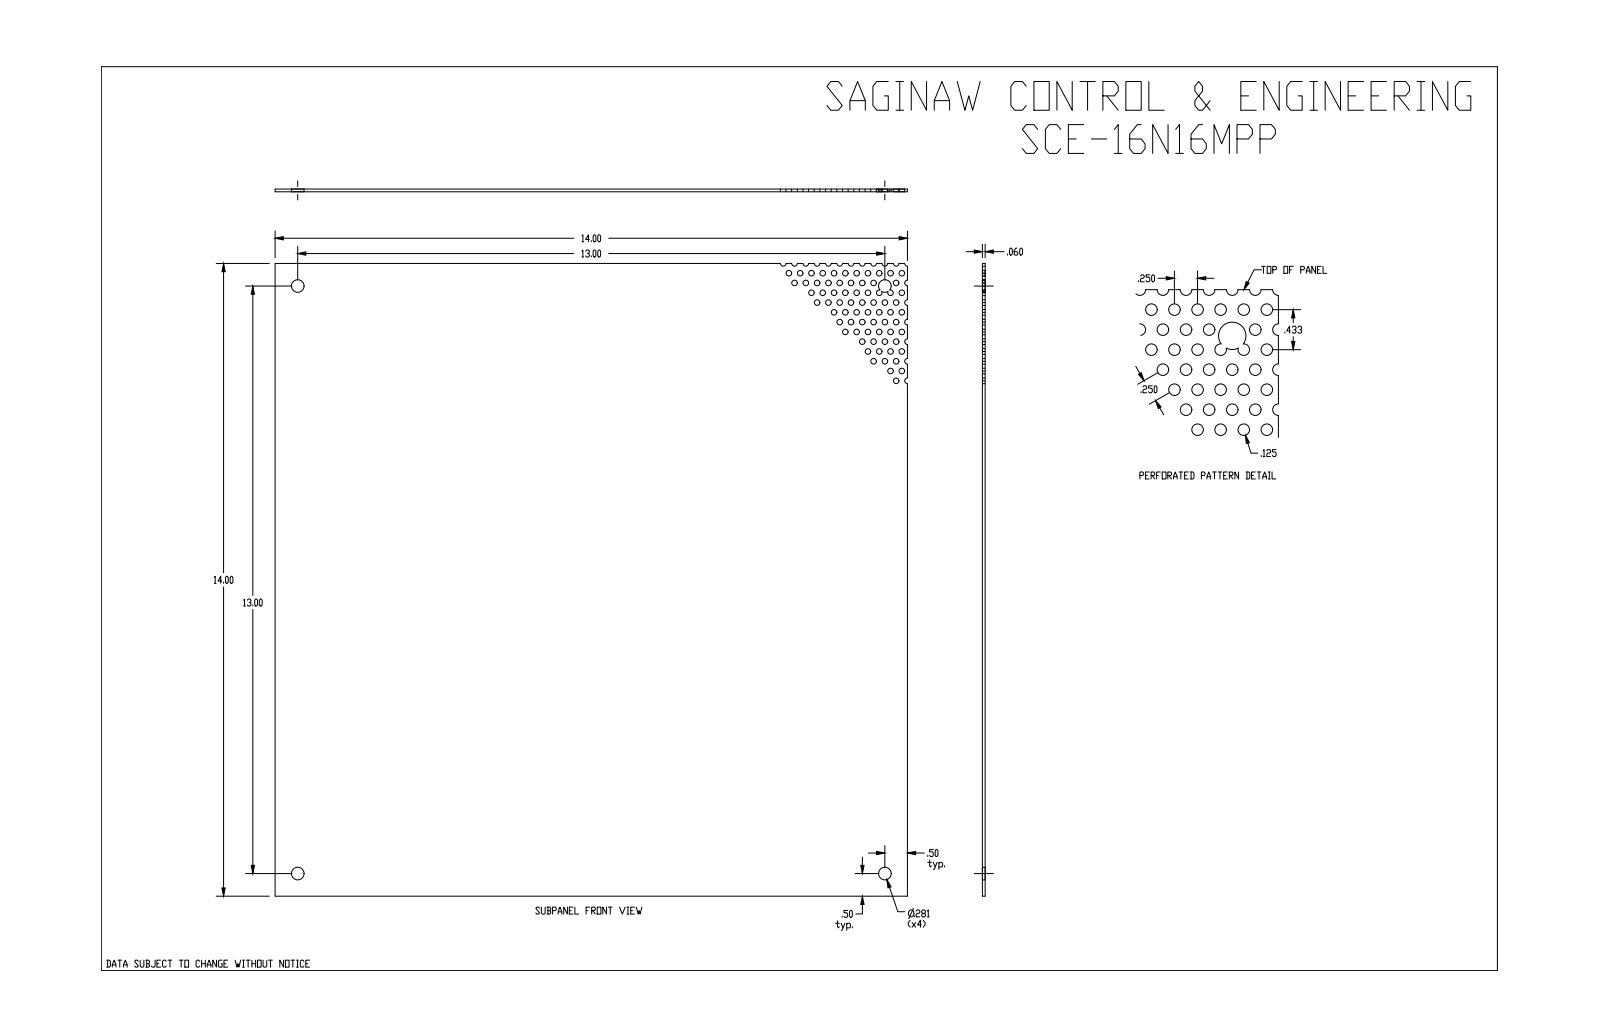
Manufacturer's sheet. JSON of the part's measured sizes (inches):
{"part_name": "SCE-16N16MPP", "step_written_by": "SolidWorks 2019 (CONFIG_CONTROL_DESIGN)", "units": "inches", "bodies": {"solids": 1, "faces": 116, "planar": 23, "cylindrical": 93, "other": 0}, "overall_size": [14, 14, 0.06], "volume_in3": 11.69, "surface_area_in2": 394.9, "round_holes": [[0.125, 66], [0.125, 4], [0.281, 4]], "partial_cylinders_radius": [[0.062, 15], [0.063, 3]], "face_to_face_distances": [0.06, 14], "hole_center_spacings": [0.25, 0.661, 0.5, 0.433, 0.433, 0.75, 0.901, 1.323]}
